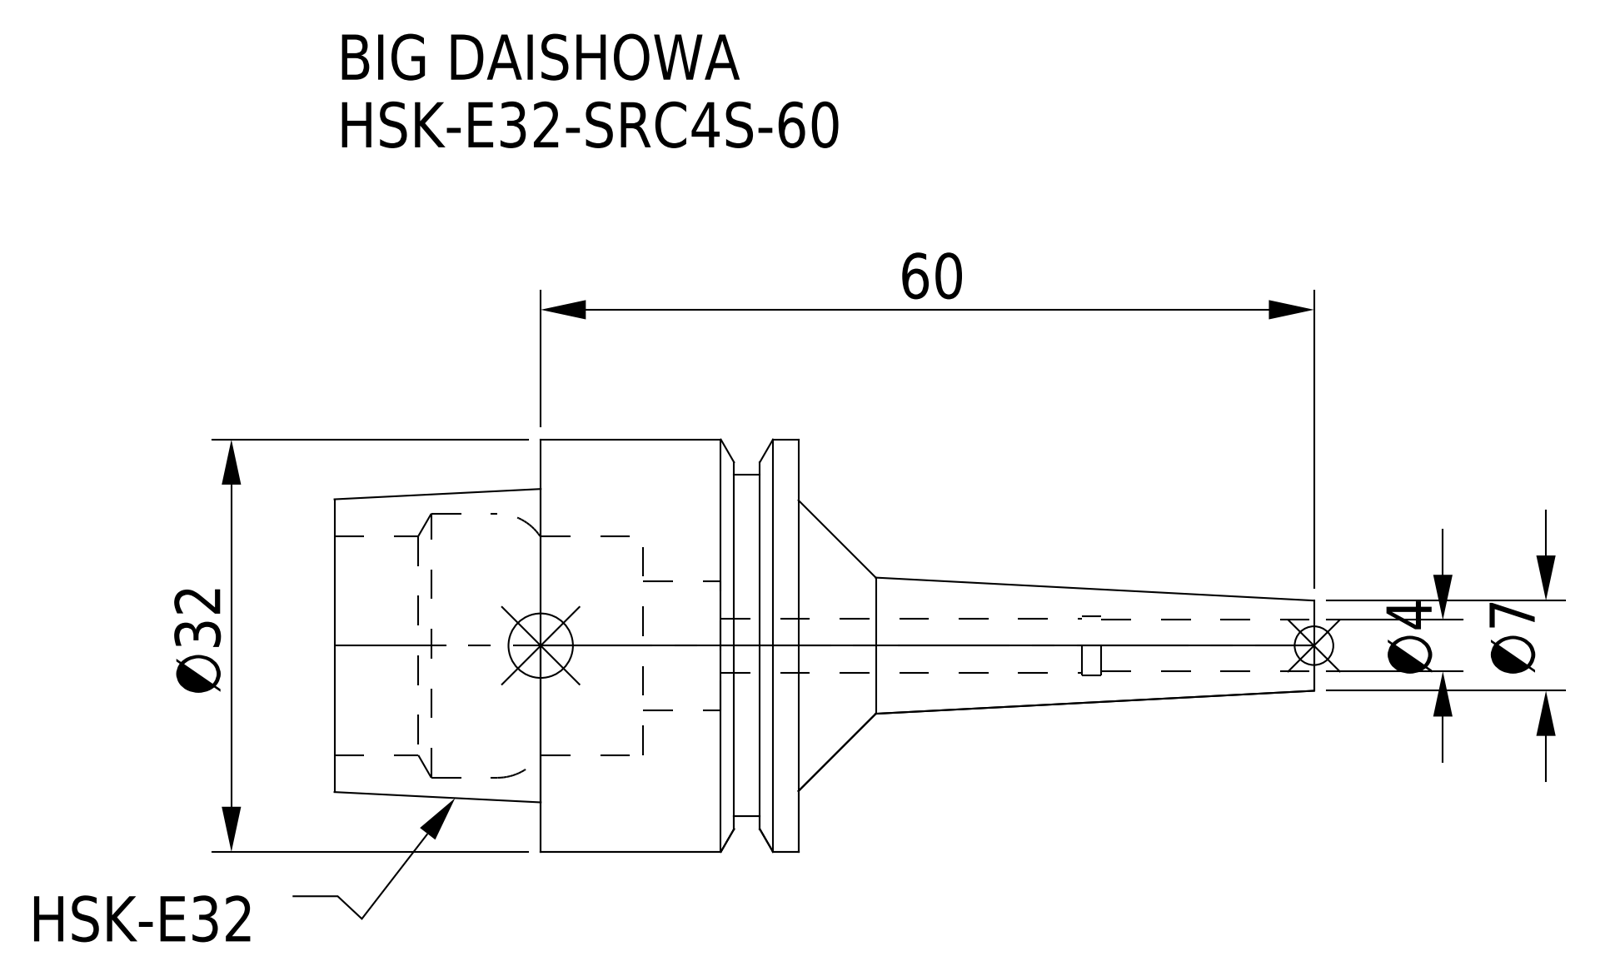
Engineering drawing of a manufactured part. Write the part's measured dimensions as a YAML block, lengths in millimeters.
part_name: "HSK-E32-SRC4S-60"
step_written_by: "CREO PARAMETRIC BY PTC INC, 2016380 (AUTOMOTIVE_DESIGN)"
units: millimeters
bodies: {solids: 1, faces: 46, planar: 10, cylindrical: 22, other: 14}
overall_size: [76, 32, 32]
volume: 18453
surface_area: 8309
round_holes:
  - {diameter: 4, count: 1}
  - {diameter: 4.2, count: 1}
  - {diameter: 4.6, count: 1}
  - {diameter: 10, count: 1}
  - {diameter: 17, count: 1}
  - {diameter: 20.5, count: 1}
round_bosses_or_shafts:
  - {diameter: 32, count: 1}
  - {diameter: 26.5, count: 1}
face_to_face_distances: [20, 36, 16, 12.05, 7.95, 23.95, 3, 9.05, 17, 33]
